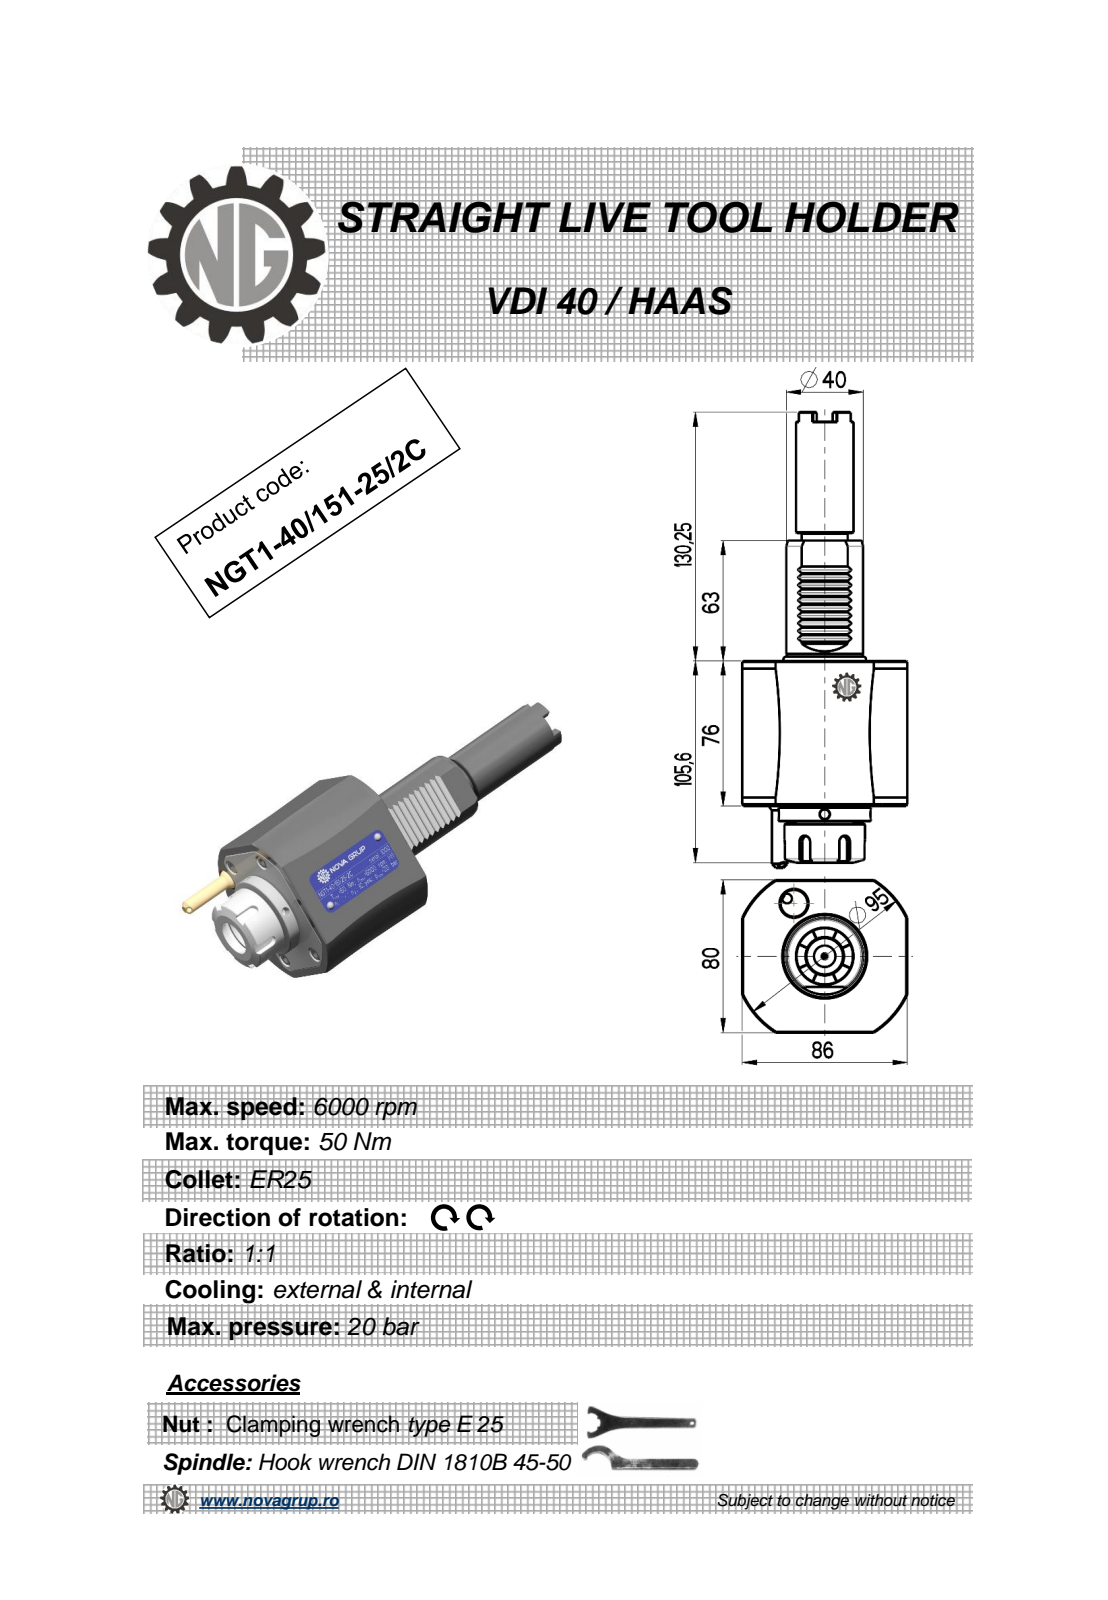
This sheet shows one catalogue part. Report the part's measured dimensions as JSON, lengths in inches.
{"part_name": "NGT1_40_151_25_1C", "step_written_by": "PRO/ENGINEER BY PARAMETRIC TECHNOLOGY CORPORATION, 2010280 (CONFIG_CONTROL_DESIGN)", "units": "inches", "bodies": {"solids": 1, "faces": 320, "planar": 133, "cylindrical": 66, "other": 121}, "overall_size": [9.393, 3.386, 3.213], "volume_in3": 38.68, "surface_area_in2": 89.85, "round_holes": [[0.197, 3], [0.118, 1], [0.768, 1]], "round_bosses_or_shafts": [[1.89, 1], [1.654, 1], [1.634, 1], [1.575, 1], [1.299, 1], [1.181, 1], [0.945, 1], [0.315, 1]], "partial_cylinders_radius": [[0.012, 10], [0.009, 6], [0.118, 5], [1.87, 1]], "face_to_face_distances": [2.992, 3.15, 3.386, 3.307, 0.315, 0.111, 0.223, 2.48, 5.472, 5.787], "hole_center_spacings": [1.575]}
